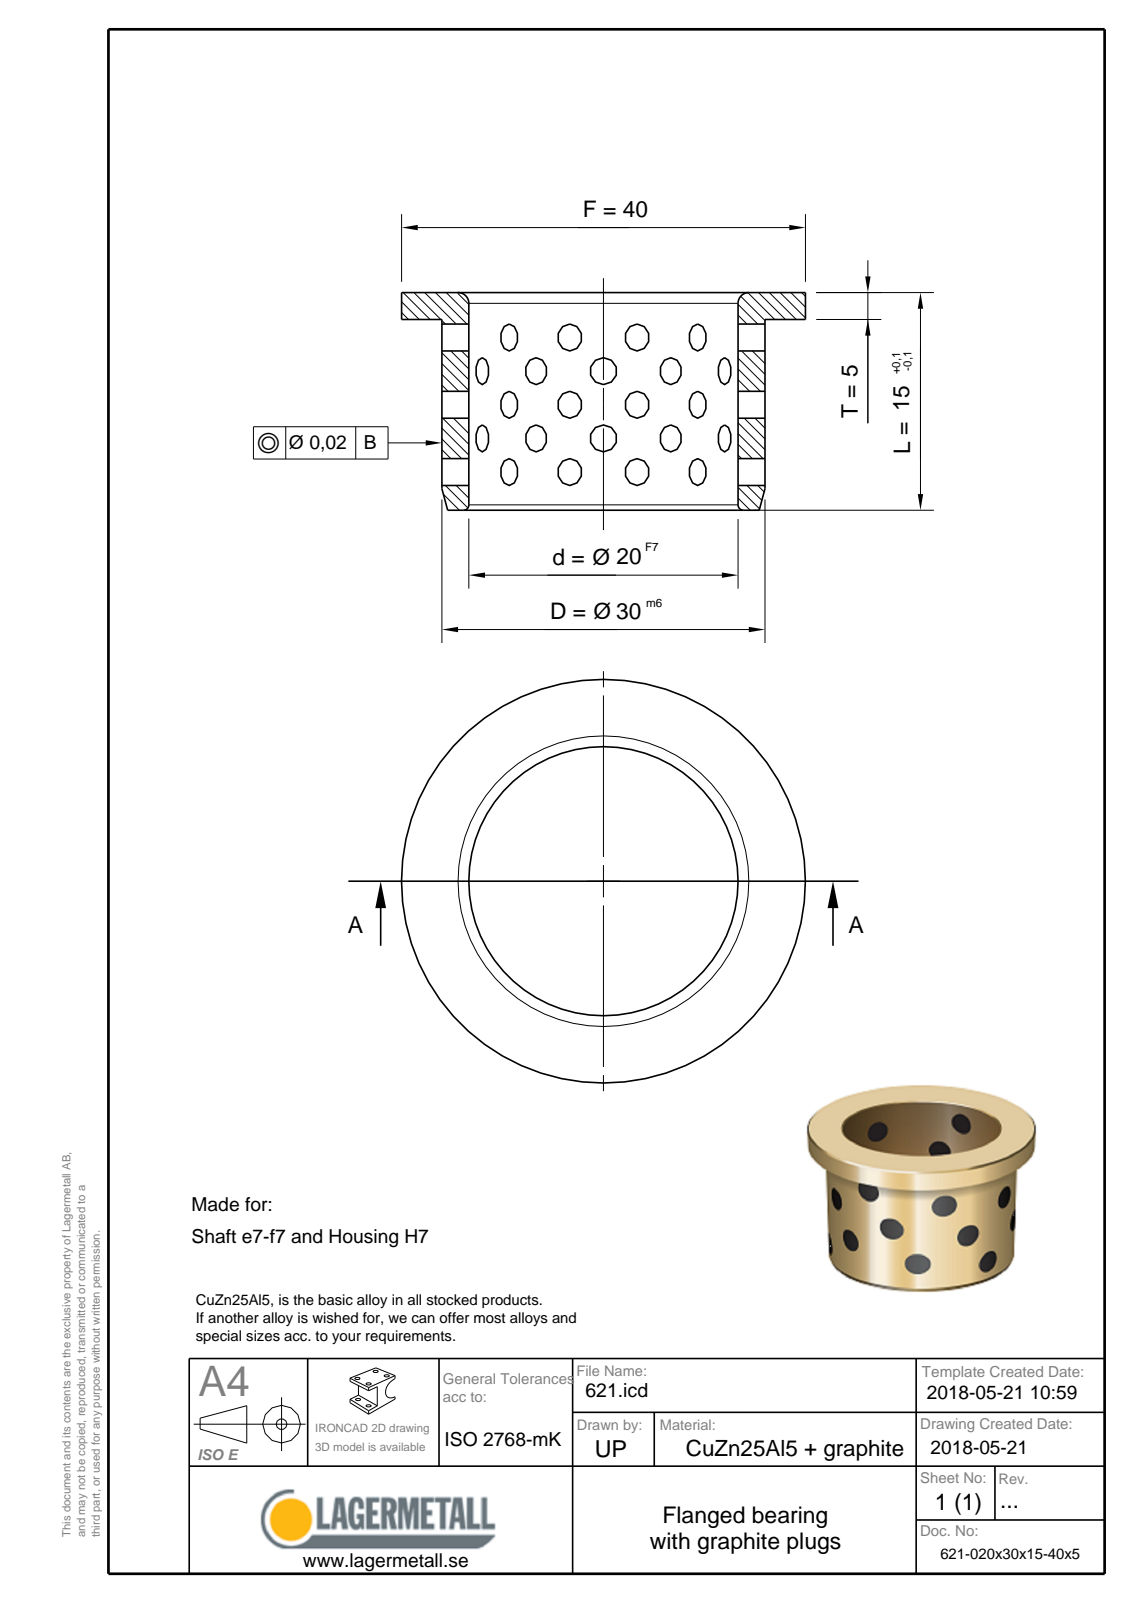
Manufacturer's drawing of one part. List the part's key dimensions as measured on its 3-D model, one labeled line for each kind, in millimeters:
Part name (STEP PRODUCT): 621-020x30x15-40x5
STEP written by: Spatial InterOp 3D (CONFIG_CONTROL_DESIGN)
Units: millimetres
Bodies: 1 solid, 9 faces (3 planar, 3 cylindrical, 3 other)
Overall size (bounding box): 40 × 40 × 15
Volume: 8 508 mm³ · Surface area: 4 257 mm²
Round holes (diameter × count): ⌀20 ×1
Round bosses / shafts (diameter × count): ⌀40 ×1, ⌀30 ×1
Main face-to-face distances: 5, 10, 15
